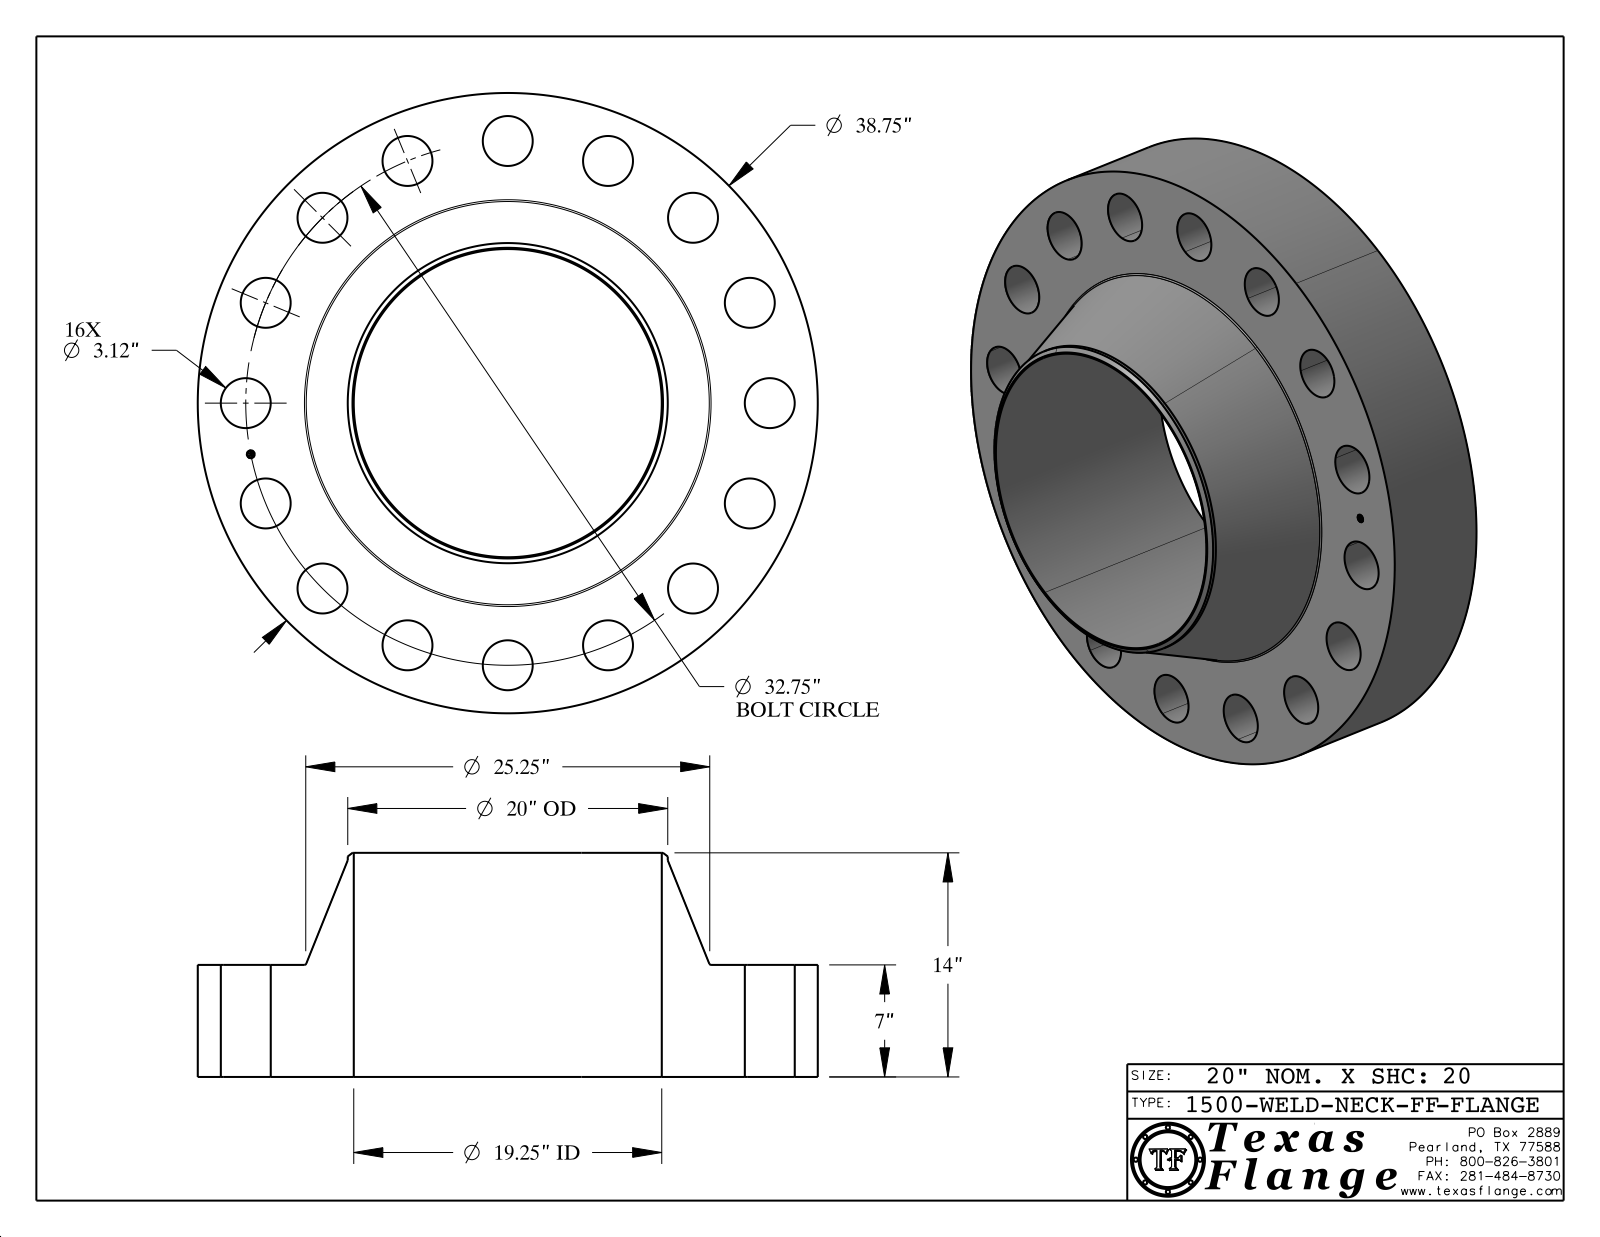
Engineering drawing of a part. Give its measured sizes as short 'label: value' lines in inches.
name: 1500-WELD-NECK-FF
written by: CATIA V5 STEP AP214 (AUTOMOTIVE_DESIGN)
unit: in
bodies: 1 solid, 432 faces (368 planar, 58 cylindrical, 6 other)
size: 38.75 × 38.75 × 14
volume: 6 108 in³; area: 4 661 in²
holes: 16× ⌀3.12, 1× ⌀0.495, 1× ⌀19.25
bosses: 8× ⌀0.03, 1× ⌀38.75, 1× ⌀20, 1× ⌀0.39
face distances: 7, 14, 6.985, 0.015, 7.015, 0.148, 0.145, 0.027, 0.096, 0.123
hole spacings: 18.195, 16.375, 12.533, 23.157, 30.257, 6.389, 6.389, 27.23
